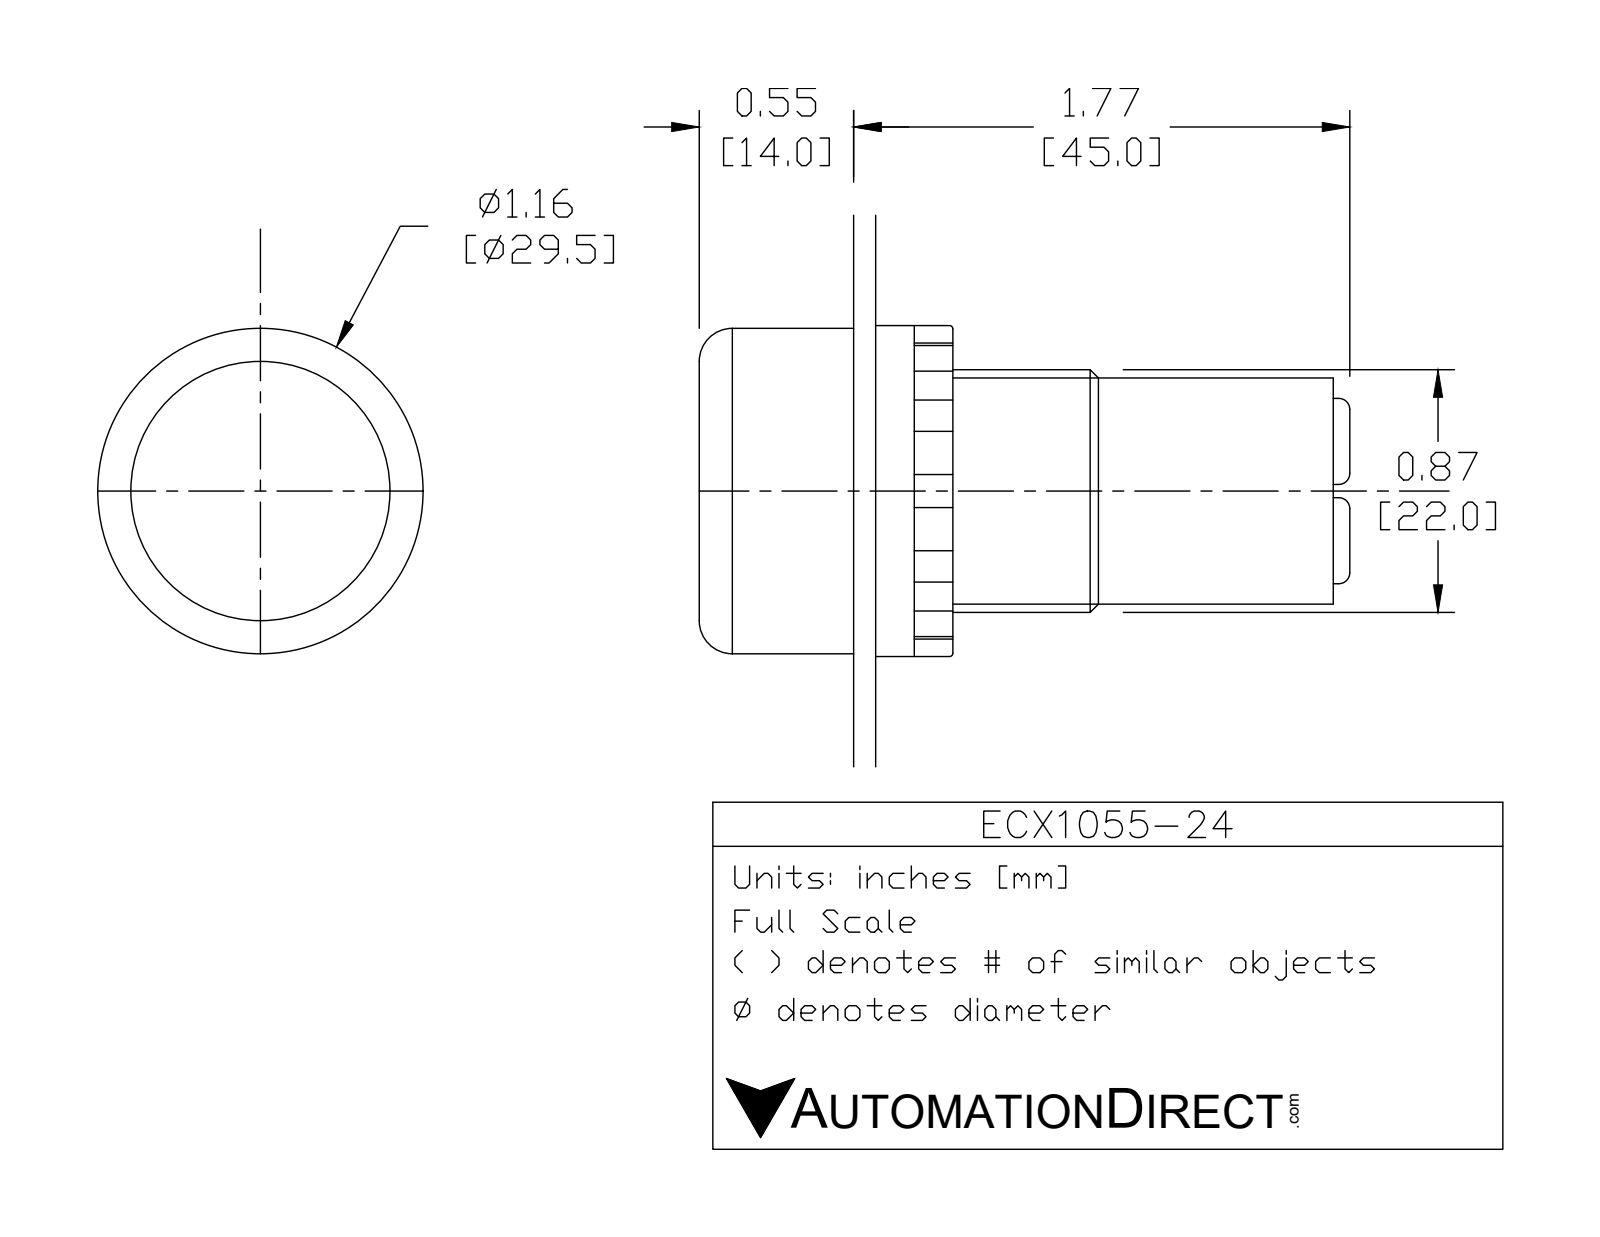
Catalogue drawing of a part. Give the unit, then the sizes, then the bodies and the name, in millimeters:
Units: millimetres
Overall size (bounding box): 59 × 30 × 30
Round holes (diameter × count): ⌀5.5 ×2, ⌀22.5 ×1
Round bosses / shafts (diameter × count): ⌀4 ×2, ⌀30 ×1, ⌀29 ×1, ⌀26.5 ×1, ⌀22 ×1, ⌀20 ×1
Partial cylindrical surfaces — rounded edges, fillets, slot ends (radius × count): R1 ×12, R9 ×1
Main face-to-face distances: 13.5, 0.5, 14, 20, 6, 6.5, 39, 7, 13, 27
Hole centre spacings: 4.62, 9.24
Volume: 26 294 mm³ · Surface area: 9 700 mm²
Bodies: 6 solids, 125 faces (63 planar, 41 cylindrical, 21 other)
Part name (STEP PRODUCT): ECX1055-24
STEP written by: SolidWorks 2017 (AUTOMOTIVE_DESIGN)
